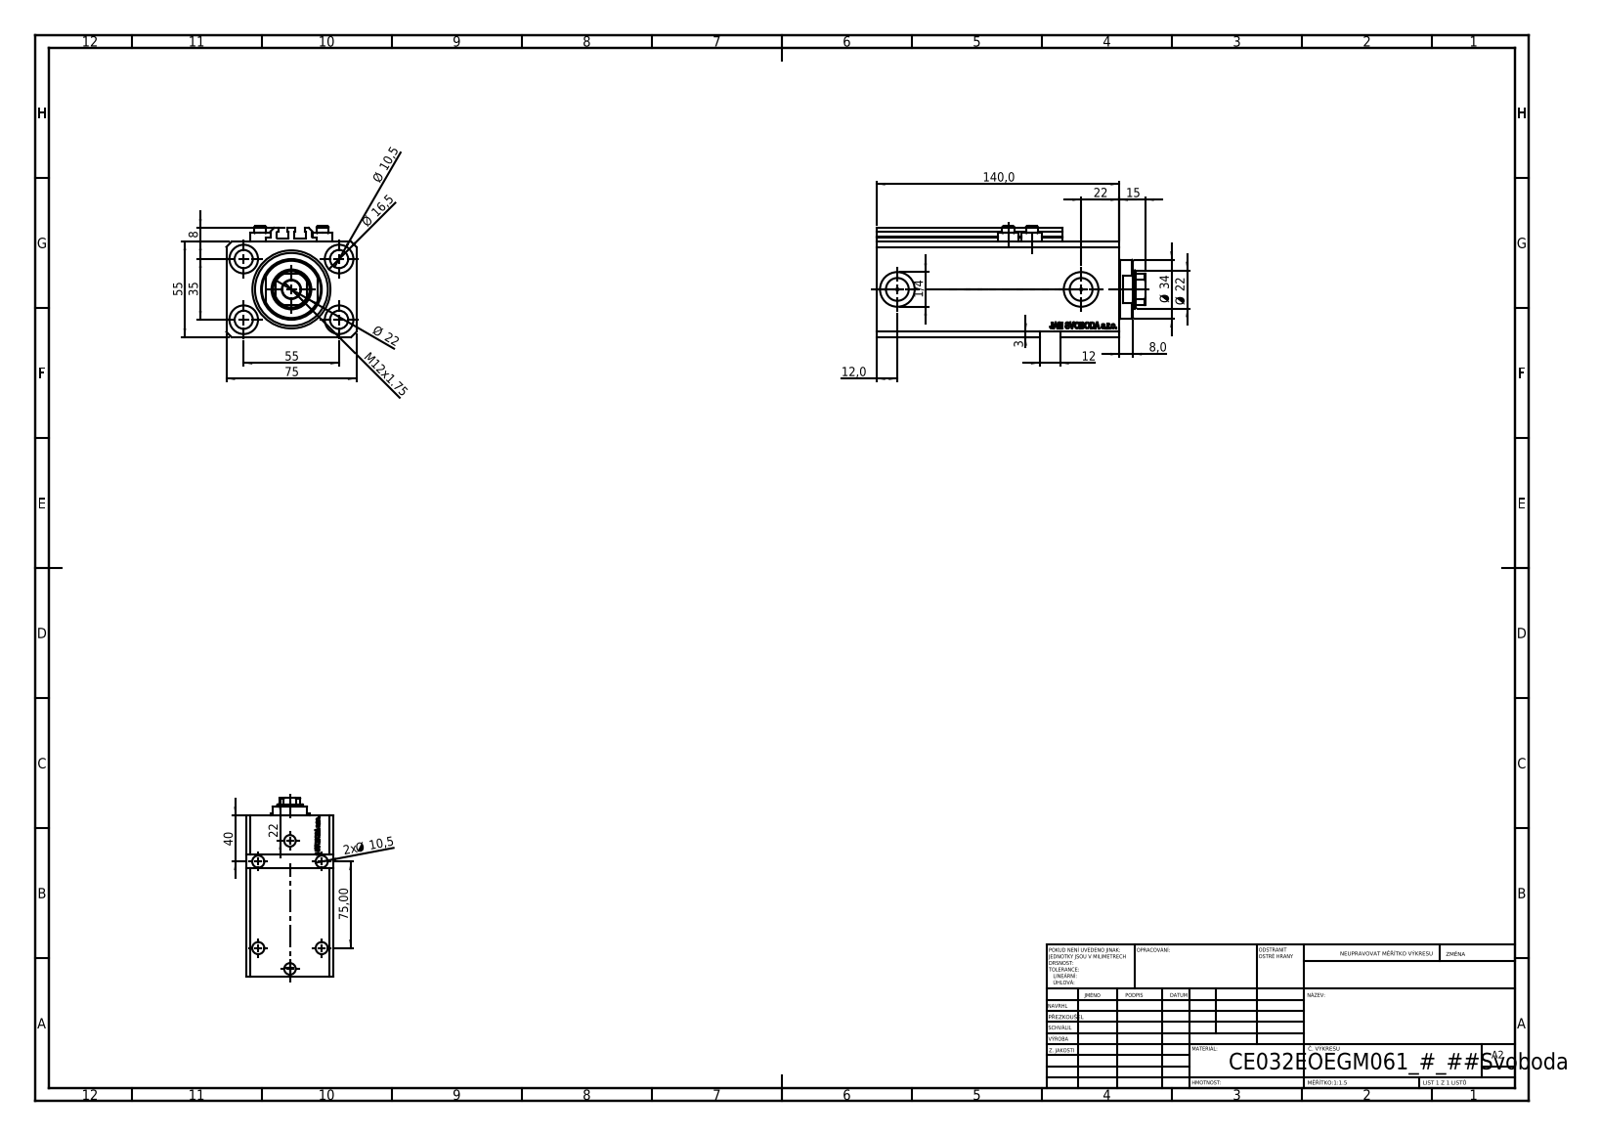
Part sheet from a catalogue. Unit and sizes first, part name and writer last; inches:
Units: inches
Overall size (bounding box): 6.102 × 2.953 × 2.52
Round holes (diameter × count): ⌀0.413 ×9, ⌀0.049 ×4, ⌀0.157 ×4, ⌀0.65 ×4, ⌀0.394 ×2, ⌀0.518 ×2, ⌀0.787 ×2, ⌀0.866 ×1, ⌀1.26 ×1, ⌀1.772 ×1
Round bosses / shafts (diameter × count): ⌀0.457 ×4, ⌀0.276 ×4, ⌀1.339 ×1
Partial cylindrical surfaces — rounded edges, fillets, slot ends (radius × count): R0.008 ×10, R0.413 ×1
Main face-to-face distances: 2.165, 2.953, 0.591, 5.512, 4.921, 0.118, 0.39, 2.244, 4.531, 5.122
Hole centre spacings: 1.283, 1.294, 2.165, 3.818, 0.535, 0.555, 1.016, 1.283
Volume: 29.61 in³ · Surface area: 178.7 in²
Bodies: 8 solids, 1084 faces (514 planar, 146 cylindrical, 424 other)
Part name (STEP PRODUCT): ALLEN BOLT V250CE; V250CE_E_Body; V250CE_C_VCP; V250CE_VC_E
STEP written by: SolidWorks 2019 (CONFIG_CONTROL_DESIGN)
